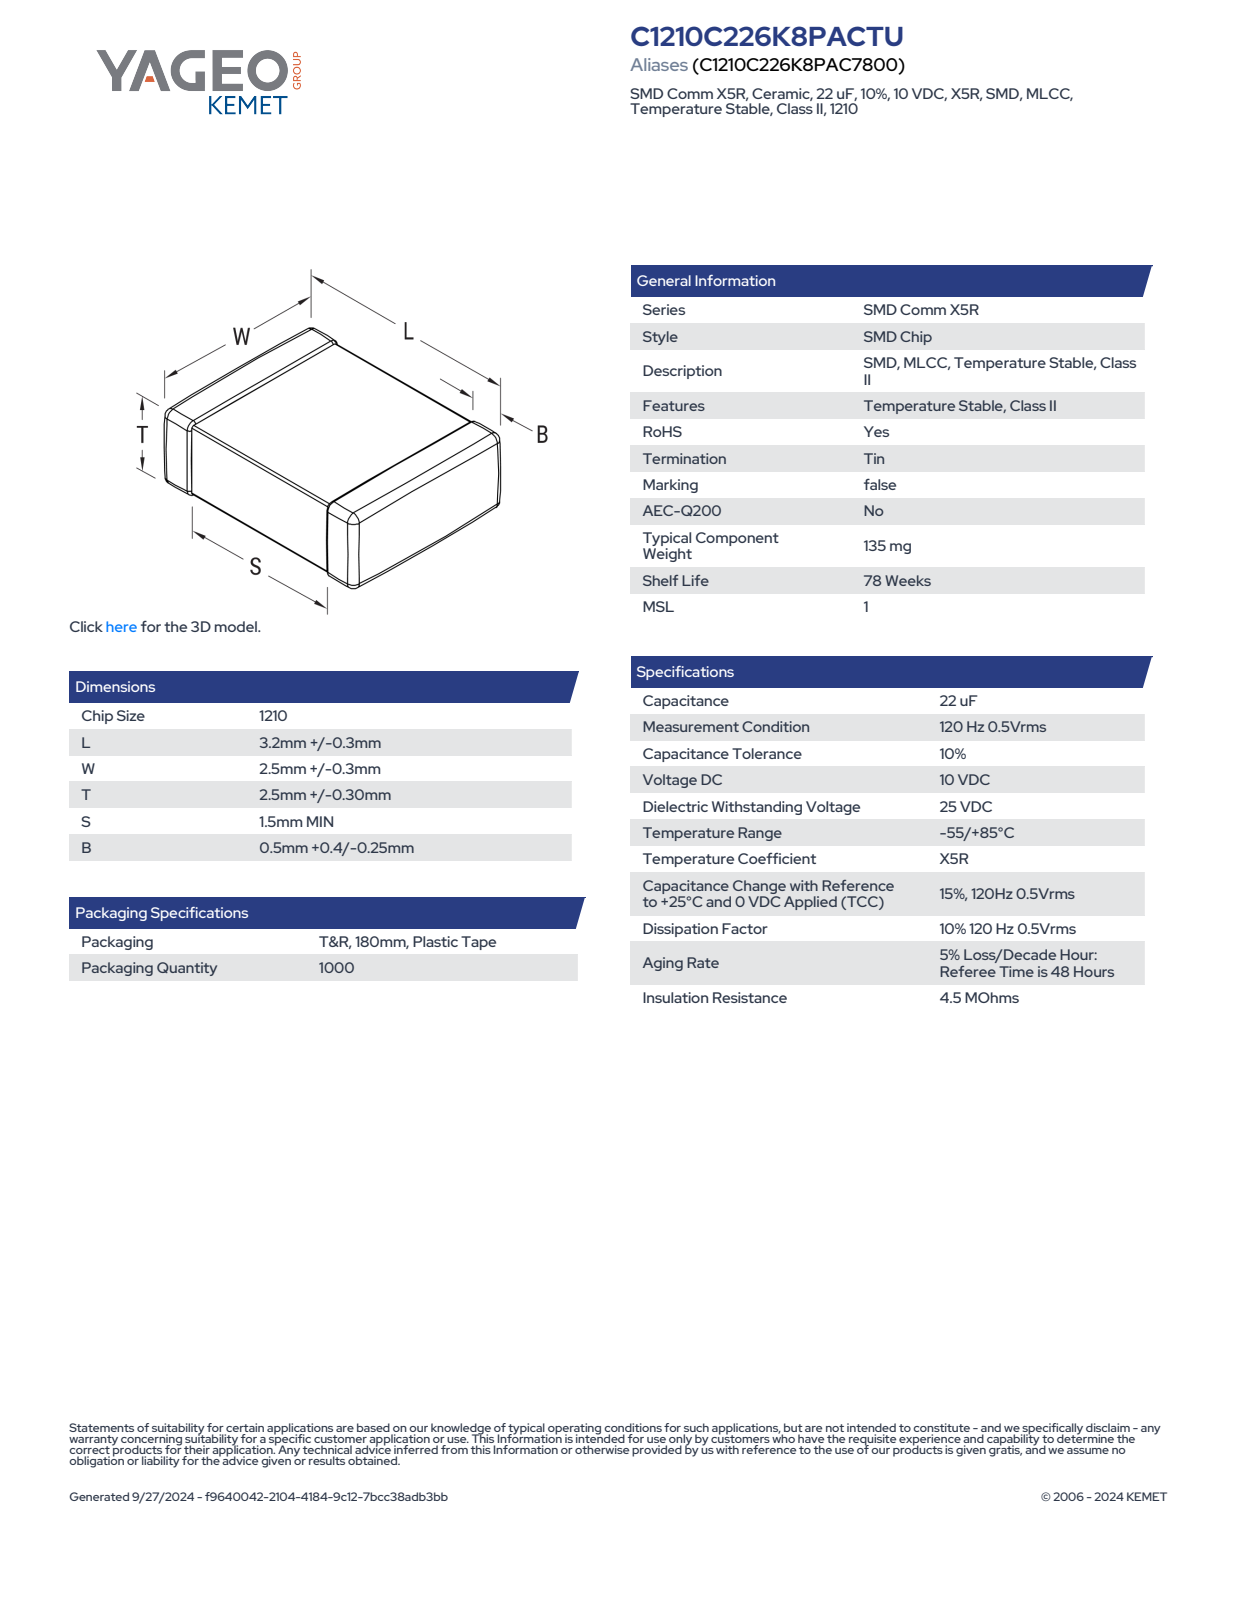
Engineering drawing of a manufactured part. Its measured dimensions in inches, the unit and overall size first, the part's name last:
Units: inches
Overall size (bounding box): 0.134 × 0.075 × 0.071
Main face-to-face distances: 0.069, 0.073, 0.068, 0.134, 0.072, 0.071, 0.075, 0.072, 0.074, 0.062
Volume: 0.001 in³ · Surface area: 0.05 in²
Bodies: 4 solids, 125 faces (71 planar, 38 cylindrical, 16 other)
Part name (STEP PRODUCT): CCS_CCSTD_1210_L3.5W2.8T2.8B0.5
STEP written by: SolidWorks 2021 (AUTOMOTIVE_DESIGN)
